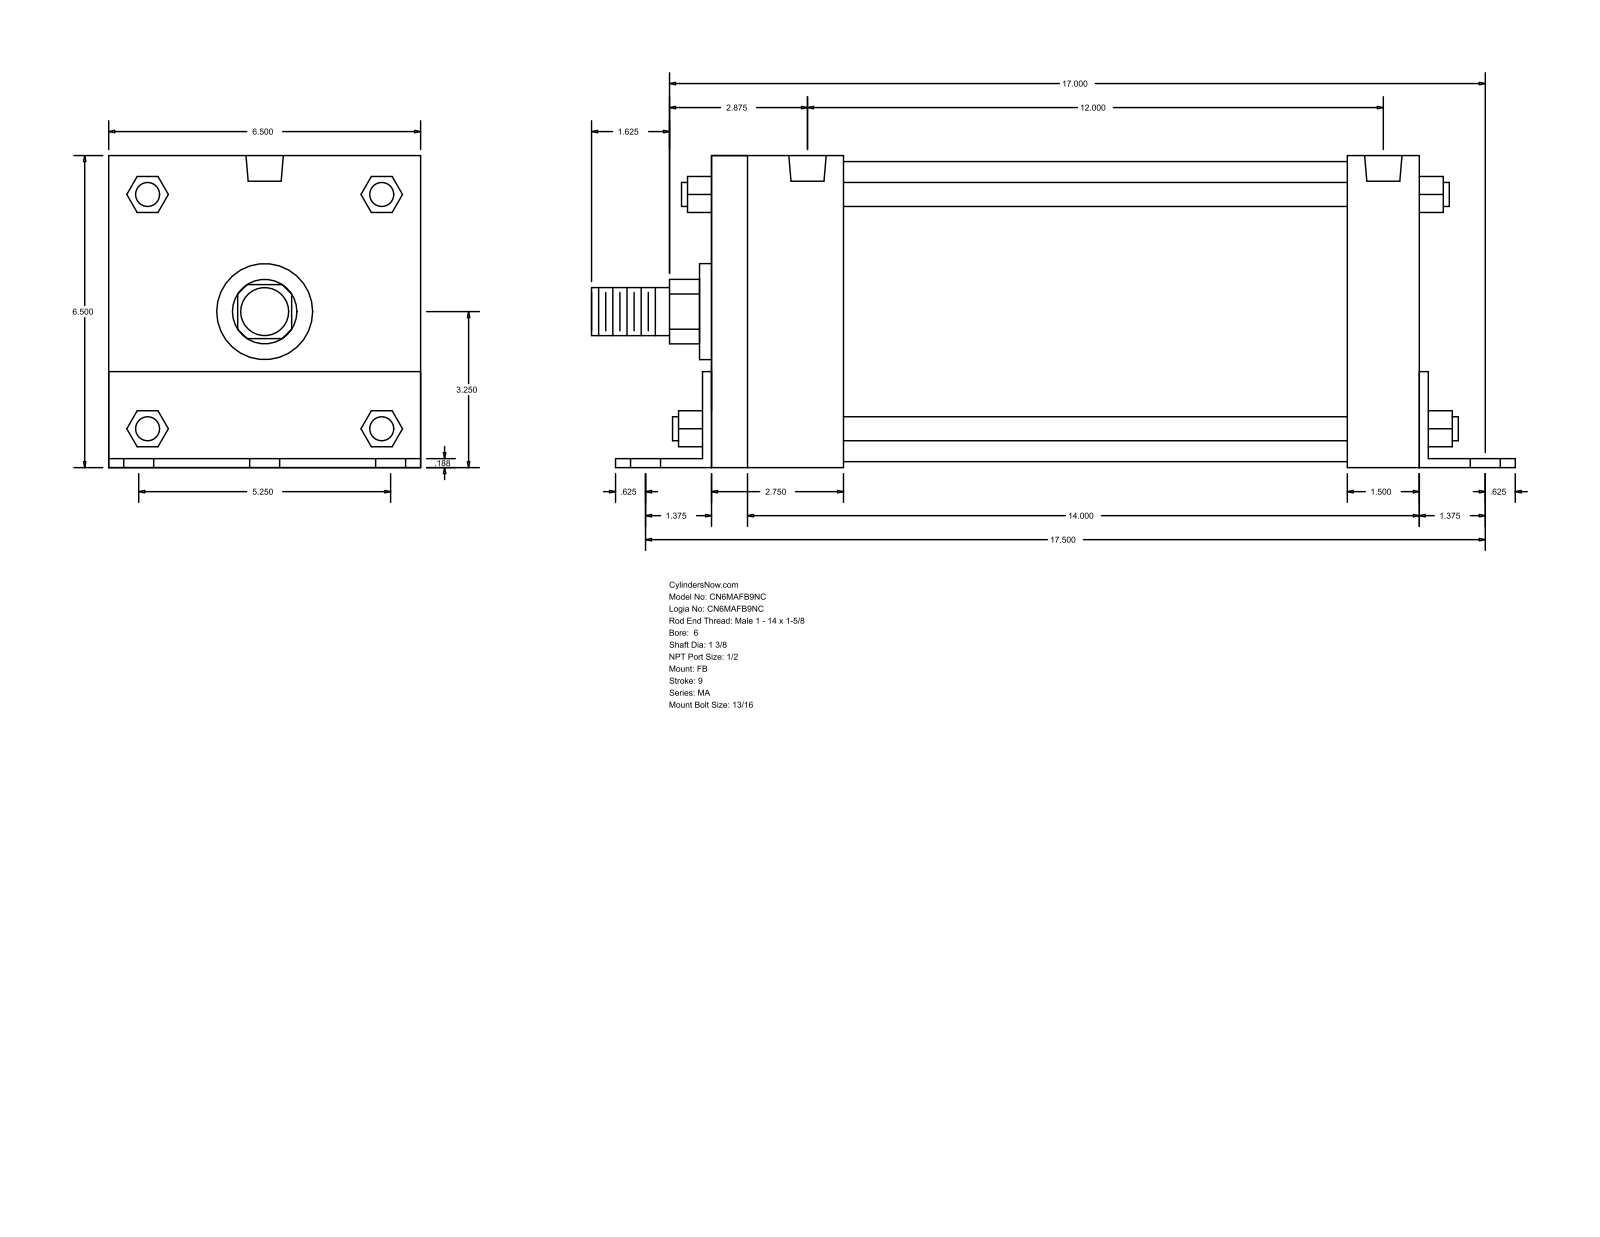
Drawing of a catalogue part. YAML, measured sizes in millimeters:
part_name: "MA_FB__0600_1.375"
step_written_by: "GSSL Pune (CONFIG_CONTROL_DESIGN)"
units: millimeters
bodies: {solids: 0, faces: 140, planar: 105, cylindrical: 35, other: 0}
overall_size: [485.77, 165.15, 165.1]
round_holes:
  - {diameter: 20.64, count: 6}
  - {diameter: 17.46, count: 4}
  - {diameter: 19.77, count: 2}
round_bosses_or_shafts:
  - {diameter: 12.7, count: 4}
  - {diameter: 158.75, count: 1}
  - {diameter: 50.8, count: 1}
  - {diameter: 34.92, count: 1}
  - {diameter: 25.4, count: 1}
partial_cylinders:
  - {radius: 17.06, count: 1}
  - {radius: 32.05, count: 1}
face_to_face_distances: [165.1, 4.76, 371.47, 165.15, 4.71, 160.39, 4.77, 38.1, 42.86, 381]
hole_center_spacings: [66.67, 446.33, 441.32, 83.82, 85.78, 108.6, 133.34, 301.62]
